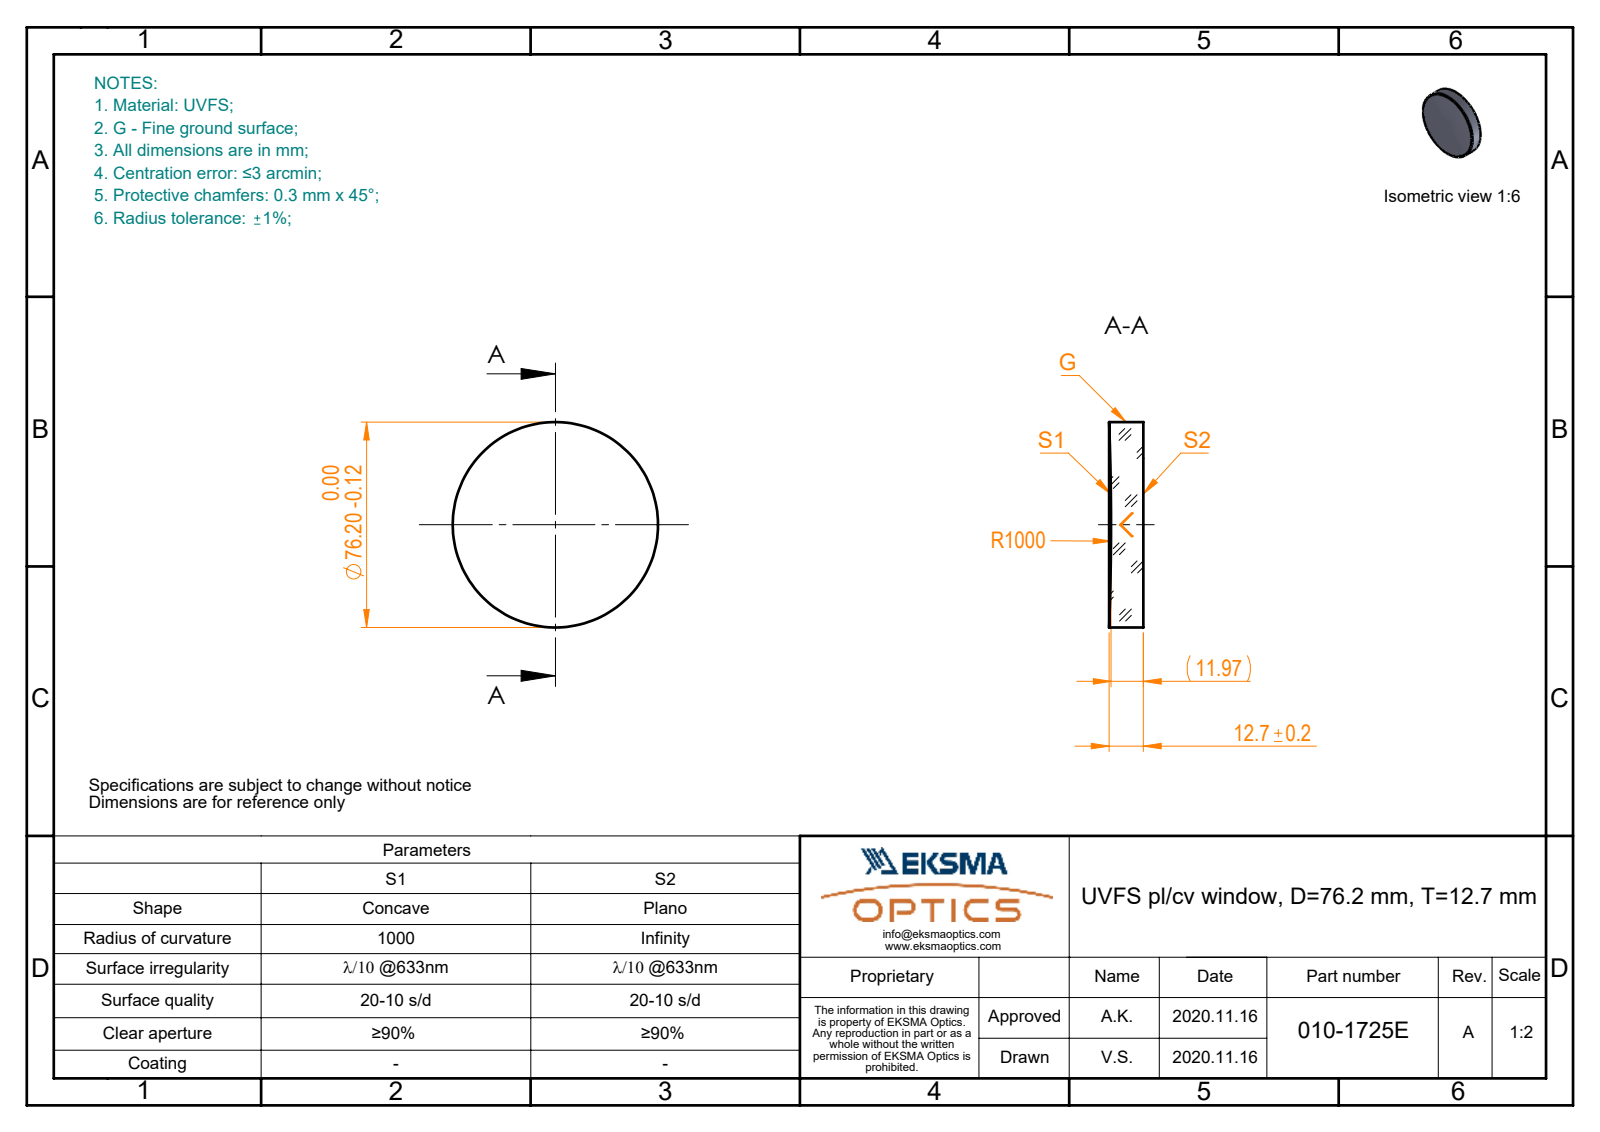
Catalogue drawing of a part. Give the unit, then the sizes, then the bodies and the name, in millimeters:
Units: millimetres
Overall size (bounding box): 76.2 × 76.2 × 12.7
Round bosses / shafts (diameter × count): ⌀76.2 ×1
Volume: 56 261 mm³ · Surface area: 12 163 mm²
Bodies: 1 solid, 5 faces (1 planar, 2 cylindrical, 2 other)
Part name (STEP PRODUCT): 010-1725E_UVFS_PCV_window
STEP written by: SolidWorks 2019 (CONFIG_CONTROL_DESIGN)
